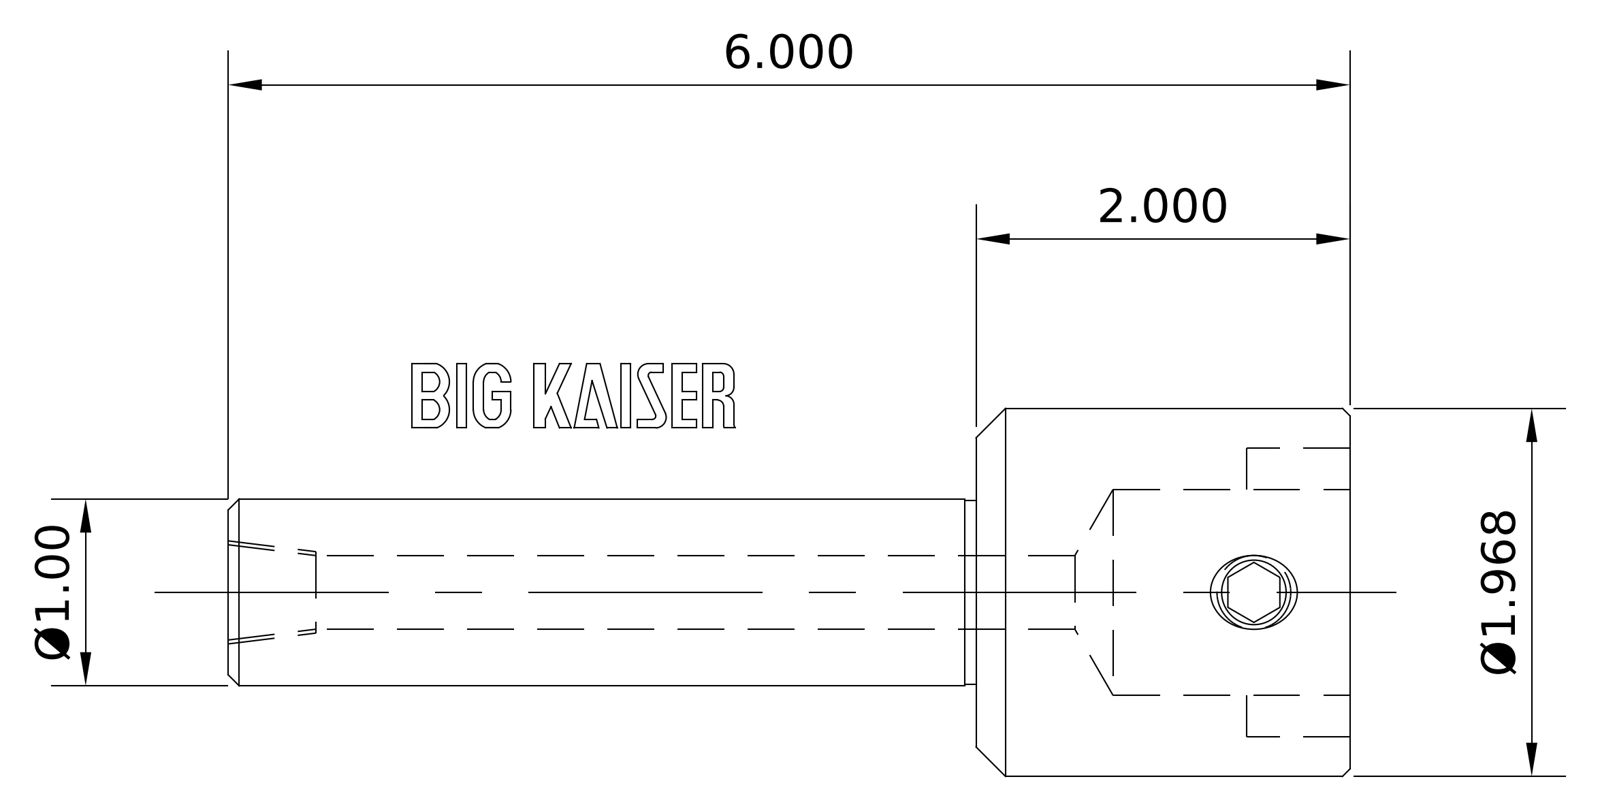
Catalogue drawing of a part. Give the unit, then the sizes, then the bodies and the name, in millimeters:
Units: millimetres
Overall size (bounding box): 152.4 × 50 × 50
Round holes (diameter × count): ⌀11.13 ×2, ⌀8.5 ×1, ⌀10.3 ×1, ⌀28 ×1, ⌀28.5 ×1
Round bosses / shafts (diameter × count): ⌀50 ×1, ⌀25.39 ×1
Partial cylindrical surfaces — rounded edges, fillets, slot ends (radius × count): R4.5 ×2
Main face-to-face distances: 50.8, 101.6, 152.4, 24.1, 138.8, 37.2, 13.6, 10.02, 14.48, 91.58
Hole centre spacings: 27.35
Volume: 109 114 mm³ · Surface area: 27 063 mm²
Bodies: 1 solid, 46 faces (20 planar, 10 cylindrical, 16 other)
Part name (STEP PRODUCT): 11.361.052
STEP written by: SolidWorks 2018 (CONFIG_CONTROL_DESIGN)
